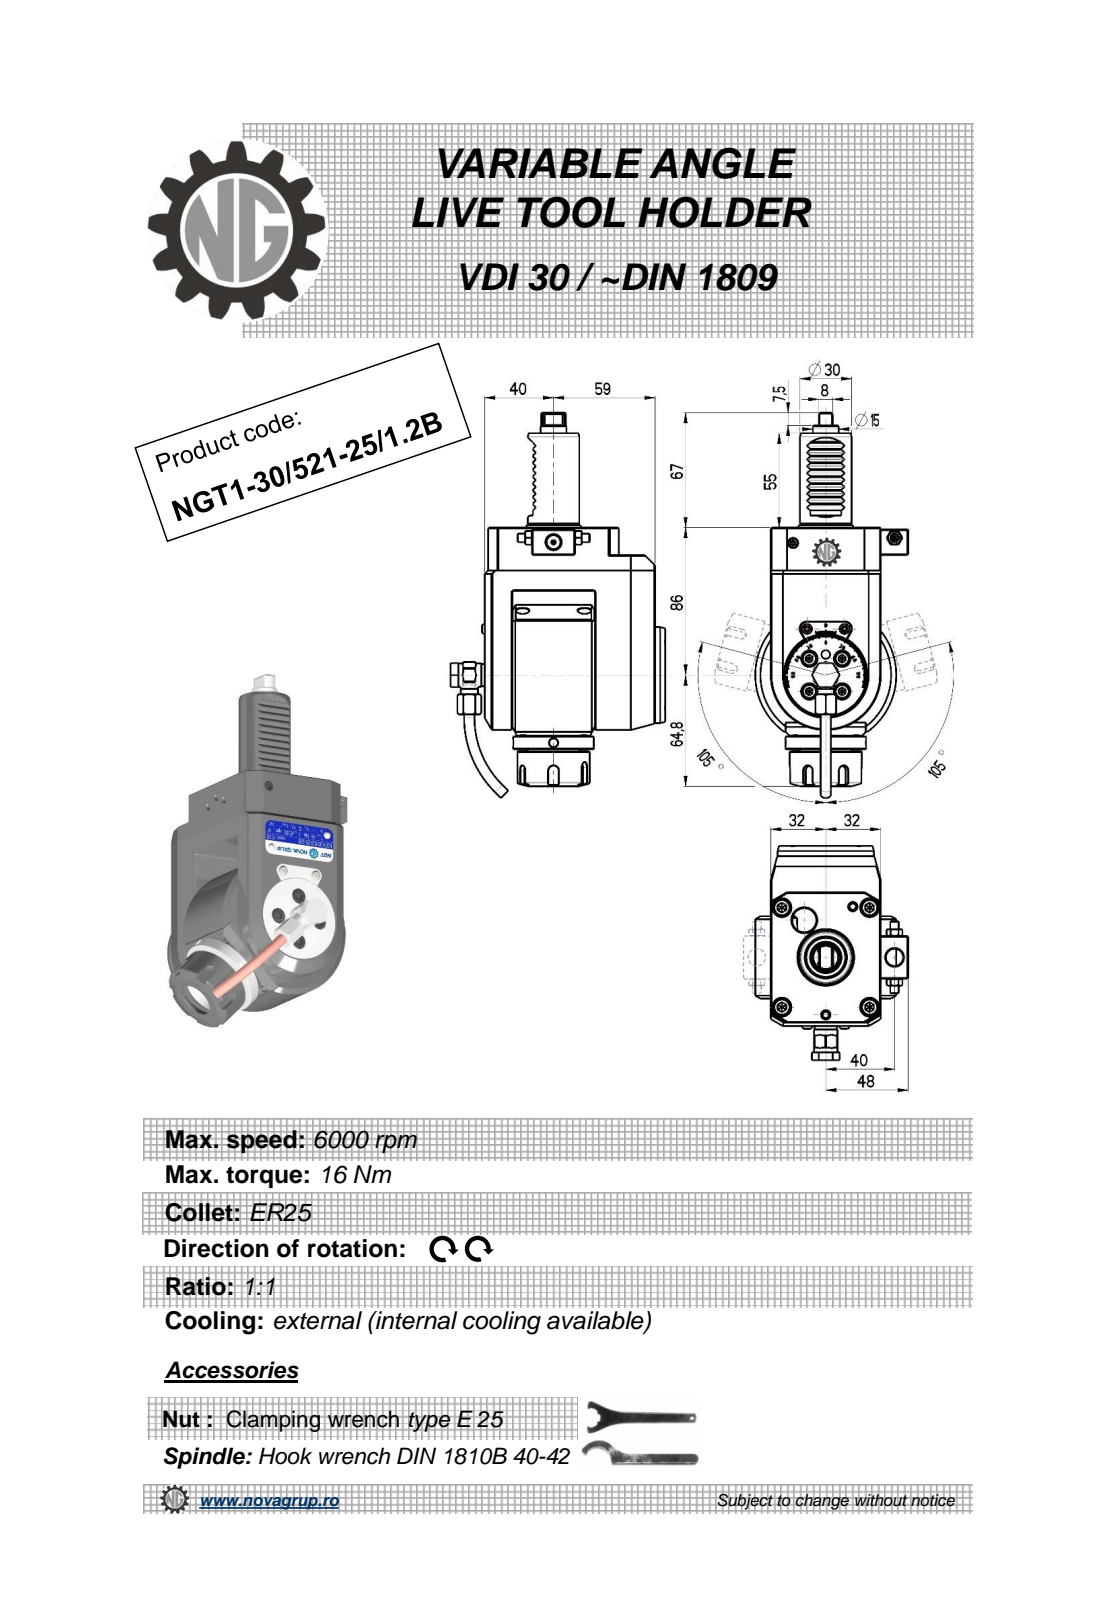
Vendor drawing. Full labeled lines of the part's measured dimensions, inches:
Part name (STEP PRODUCT): NGT1_30_521_25_1_2B
STEP written by: PRO/ENGINEER BY PARAMETRIC TECHNOLOGY CORPORATION, 2010280 (CONFIG_CONTROL_DESIGN)
Units: inches
Bodies: 1 solid, 565 faces (239 planar, 138 cylindrical, 188 other)
Overall size (bounding box): 8.845 × 4.917 × 3.504
Volume: 47.97 in³ · Surface area: 117 in²
Round holes (diameter × count): ⌀0.157 ×3, ⌀0.197 ×2, ⌀0.118 ×1, ⌀0.165 ×1, ⌀0.244 ×1, ⌀0.354 ×1, ⌀0.374 ×1, ⌀0.394 ×1, ⌀0.433 ×1, ⌀0.799 ×1
Round bosses / shafts (diameter × count): ⌀0.394 ×2, ⌀0.236 ×2, ⌀0.224 ×2, ⌀3.228 ×1, ⌀2.205 ×1, ⌀1.85 ×1, ⌀1.654 ×1, ⌀1.378 ×1
Partial cylindrical surfaces — rounded edges, fillets, slot ends (radius × count): R0.01 ×12, R0.012 ×10, R0.006 ×6, R0.118 ×5, R0.02 ×4, R0.031 ×2, R0.039 ×2, R0.283 ×1
Main face-to-face distances: 2.52, 0.63, 1.457, 0.236, 3.898, 4.134, 0.551, 0.827, 1.378, 3.268
Hole centre spacings: 0.016, 1.553, 1.575, 1.929, 1.945, 2.49, 2.502, 3.521
